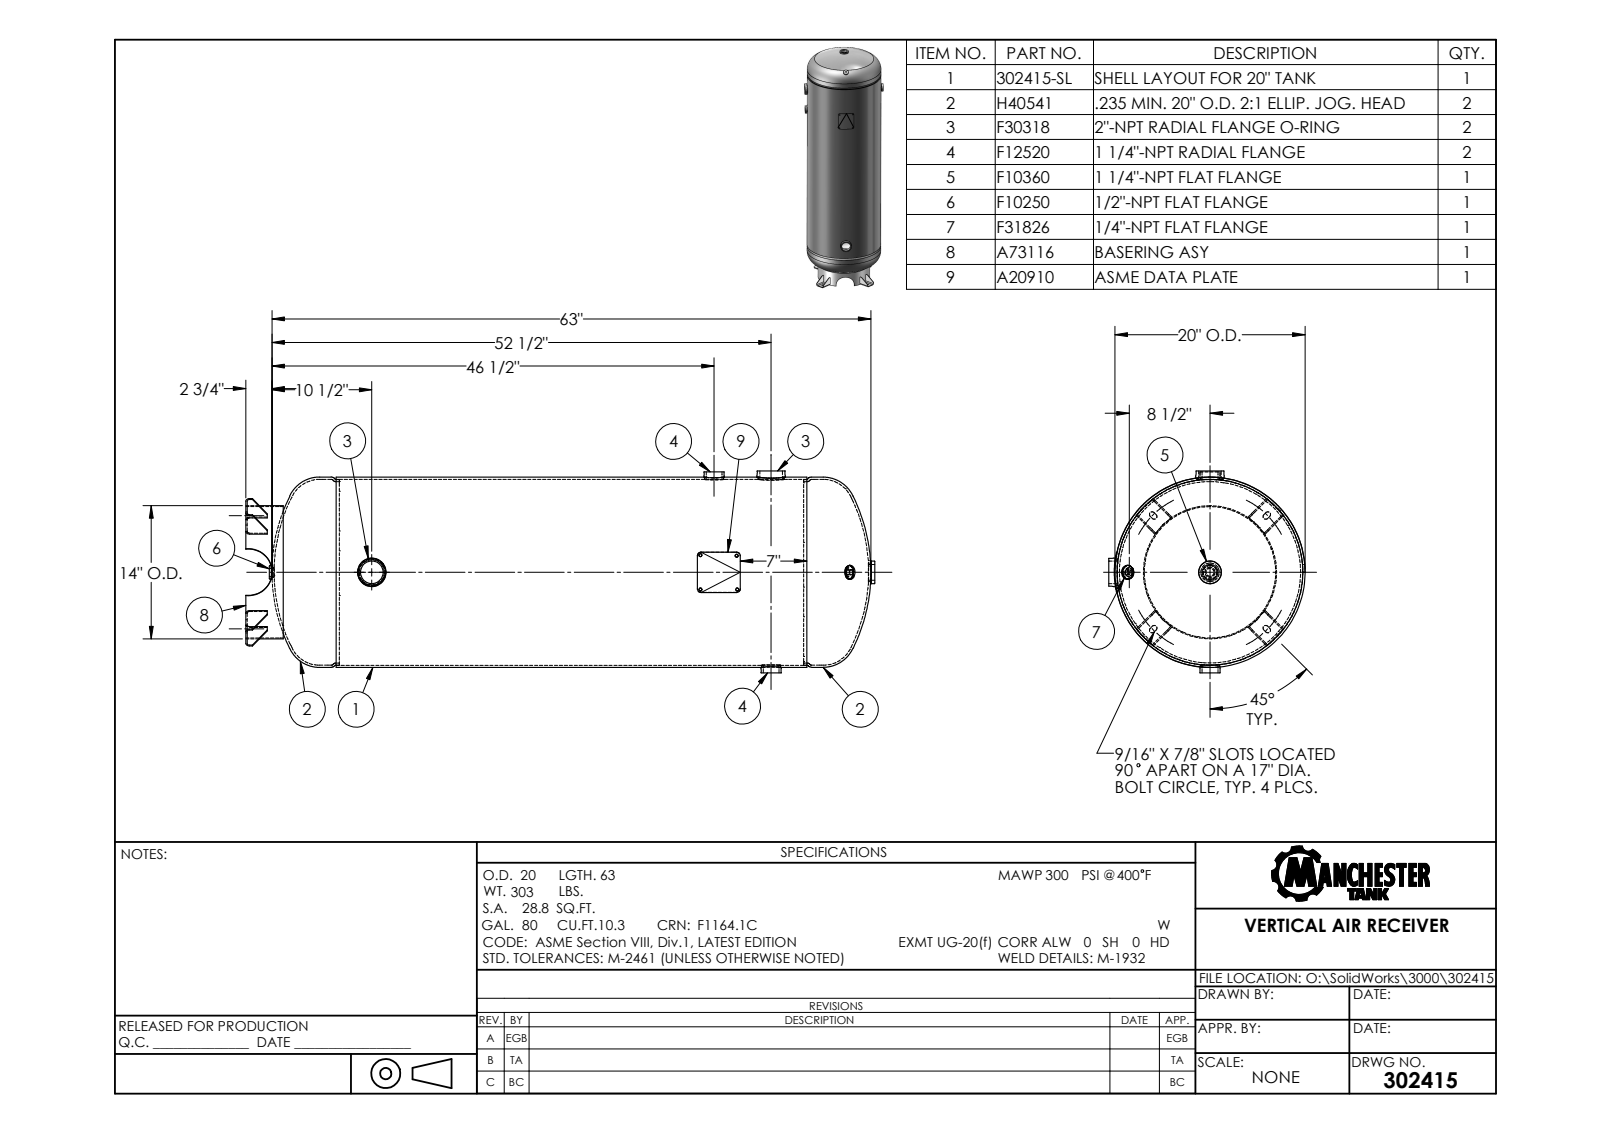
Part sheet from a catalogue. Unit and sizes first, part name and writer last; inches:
Units: inches
Overall size (bounding box): 66.003 × 21.572 × 20.832
Round holes (diameter × count): ⌀1.66 ×3, ⌀2.375 ×2, ⌀0.54 ×1, ⌀0.84 ×1, ⌀13.79 ×1, ⌀19 ×1, ⌀19.546 ×1
Round bosses / shafts (diameter × count): ⌀3.625 ×2, ⌀2.75 ×2, ⌀20 ×1, ⌀19.5 ×1, ⌀14 ×1, ⌀2.38 ×1, ⌀2.375 ×1, ⌀1.813 ×1
Partial cylindrical surfaces — rounded edges, fillets, slot ends (radius × count): R0.25 ×8, R0.281 ×8, R0.384 ×8, R10.06 ×1
Main face-to-face distances: 0.134, 2.383, 58.356, 58.49, 0.325, 58.681, 58.815, 49.5, 49.175, 9.181
Hole centre spacings: 6
Bodies: 0 solids, 252 faces (100 planar, 73 cylindrical, 79 other)
Part name (STEP PRODUCT): 302415
STEP written by: SolidWorks 2011 (CONFIG_CONTROL_DESIGN)
